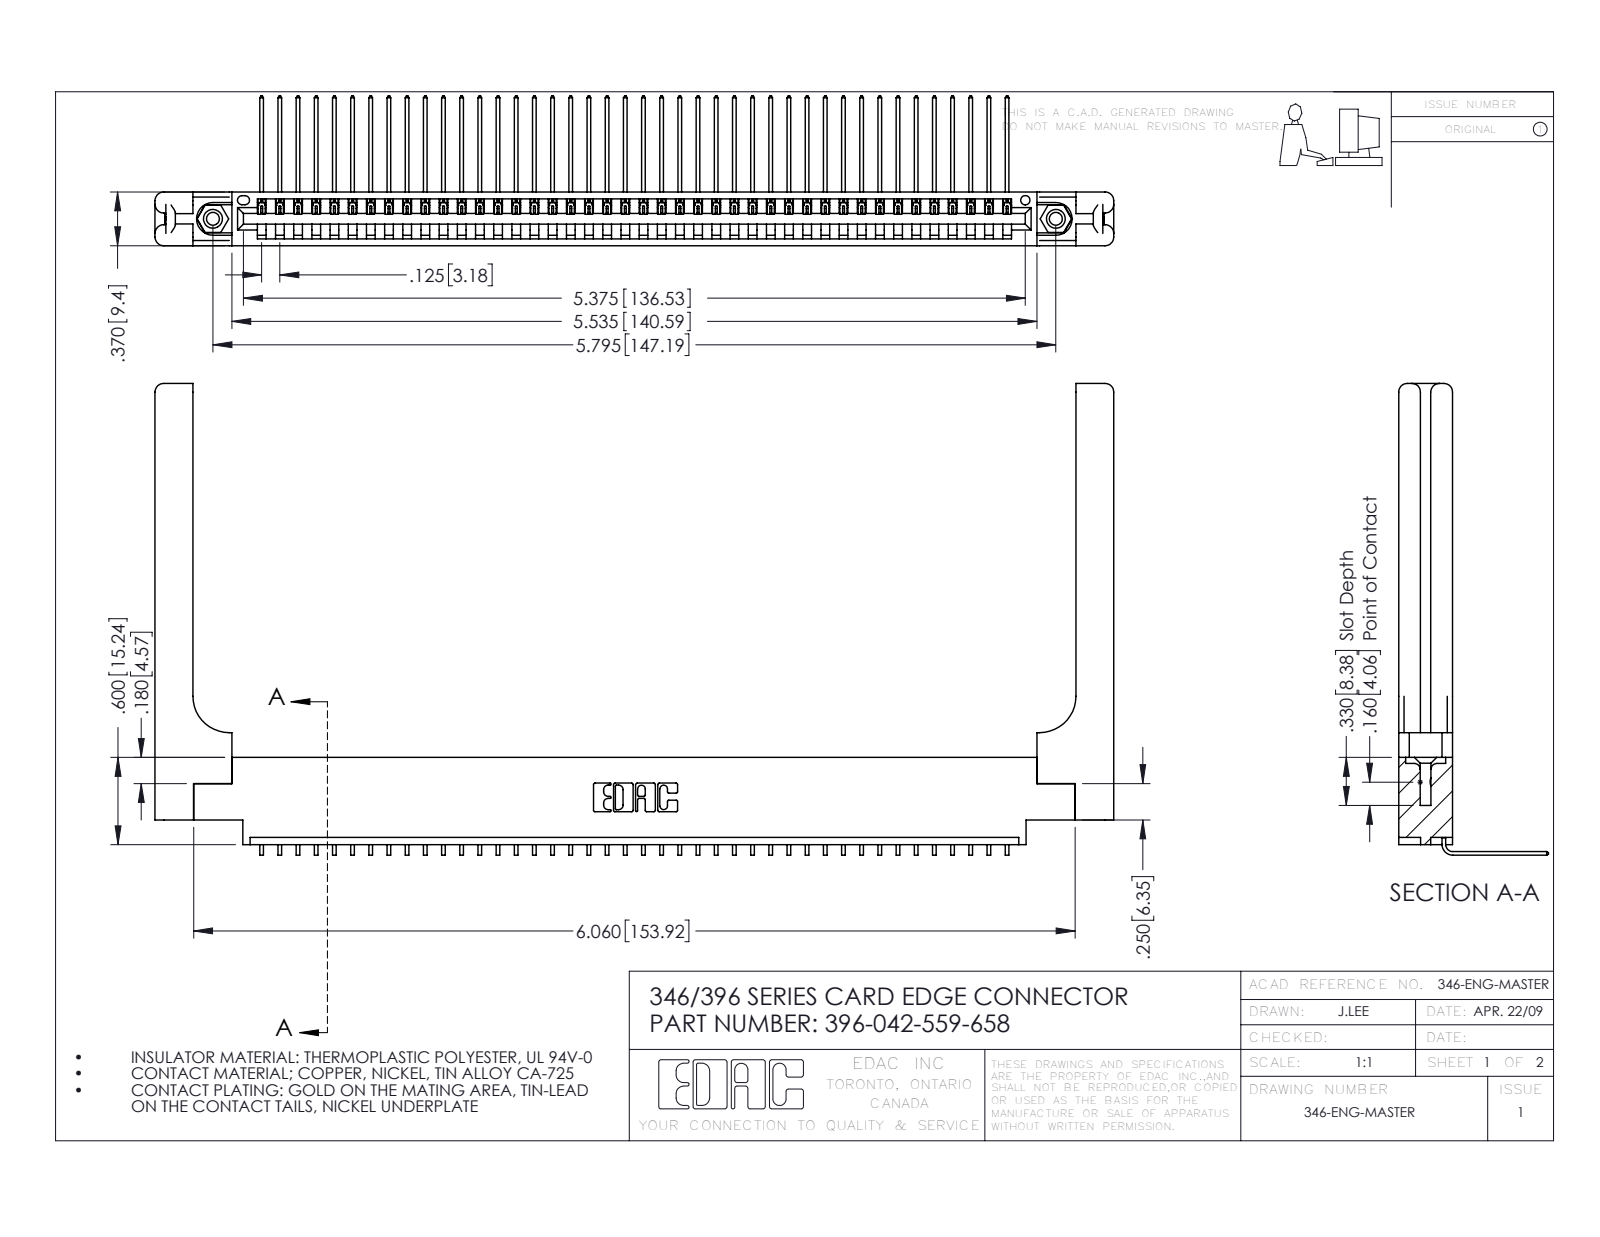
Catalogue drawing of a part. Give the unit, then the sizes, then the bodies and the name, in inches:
Units: inches
Overall size (bounding box): 6.591 × 3.243 × 1.03
Round holes (diameter × count): ⌀0.089 ×2, ⌀0.125 ×2, ⌀0.156 ×2, ⌀0.064 ×1
Round bosses / shafts (diameter × count): ⌀0.155 ×2
Partial cylindrical surfaces — rounded edges, fillets, slot ends (radius × count): R0.006 ×84, R0.01 ×22, R0.06 ×16, R0.007 ×6, R0.031 ×6, R0.026 ×3, R0.03 ×2, R0.031 ×2
Main face-to-face distances: 0.37, 0.048, 0.322, 0.072, 0.148, 0.15, 0.025, 0.25, 0.298, 0.222
Hole centre spacings: 0.246, 5.586, 5.795
Volume: 1.436 in³ · Surface area: 40.57 in²
Bodies: 47 solids, 2902 faces (1992 planar, 850 cylindrical, 60 other)
Part name (STEP PRODUCT): 396-042-559-658; 346-220-058_345-220-058; 345-250-001_345-250-001-102; 346 Part_0.170 Offset - 0.156 Dia-TH (+1 more)
STEP written by: SolidWorks 2016 (CONFIG_CONTROL_DESIGN)
